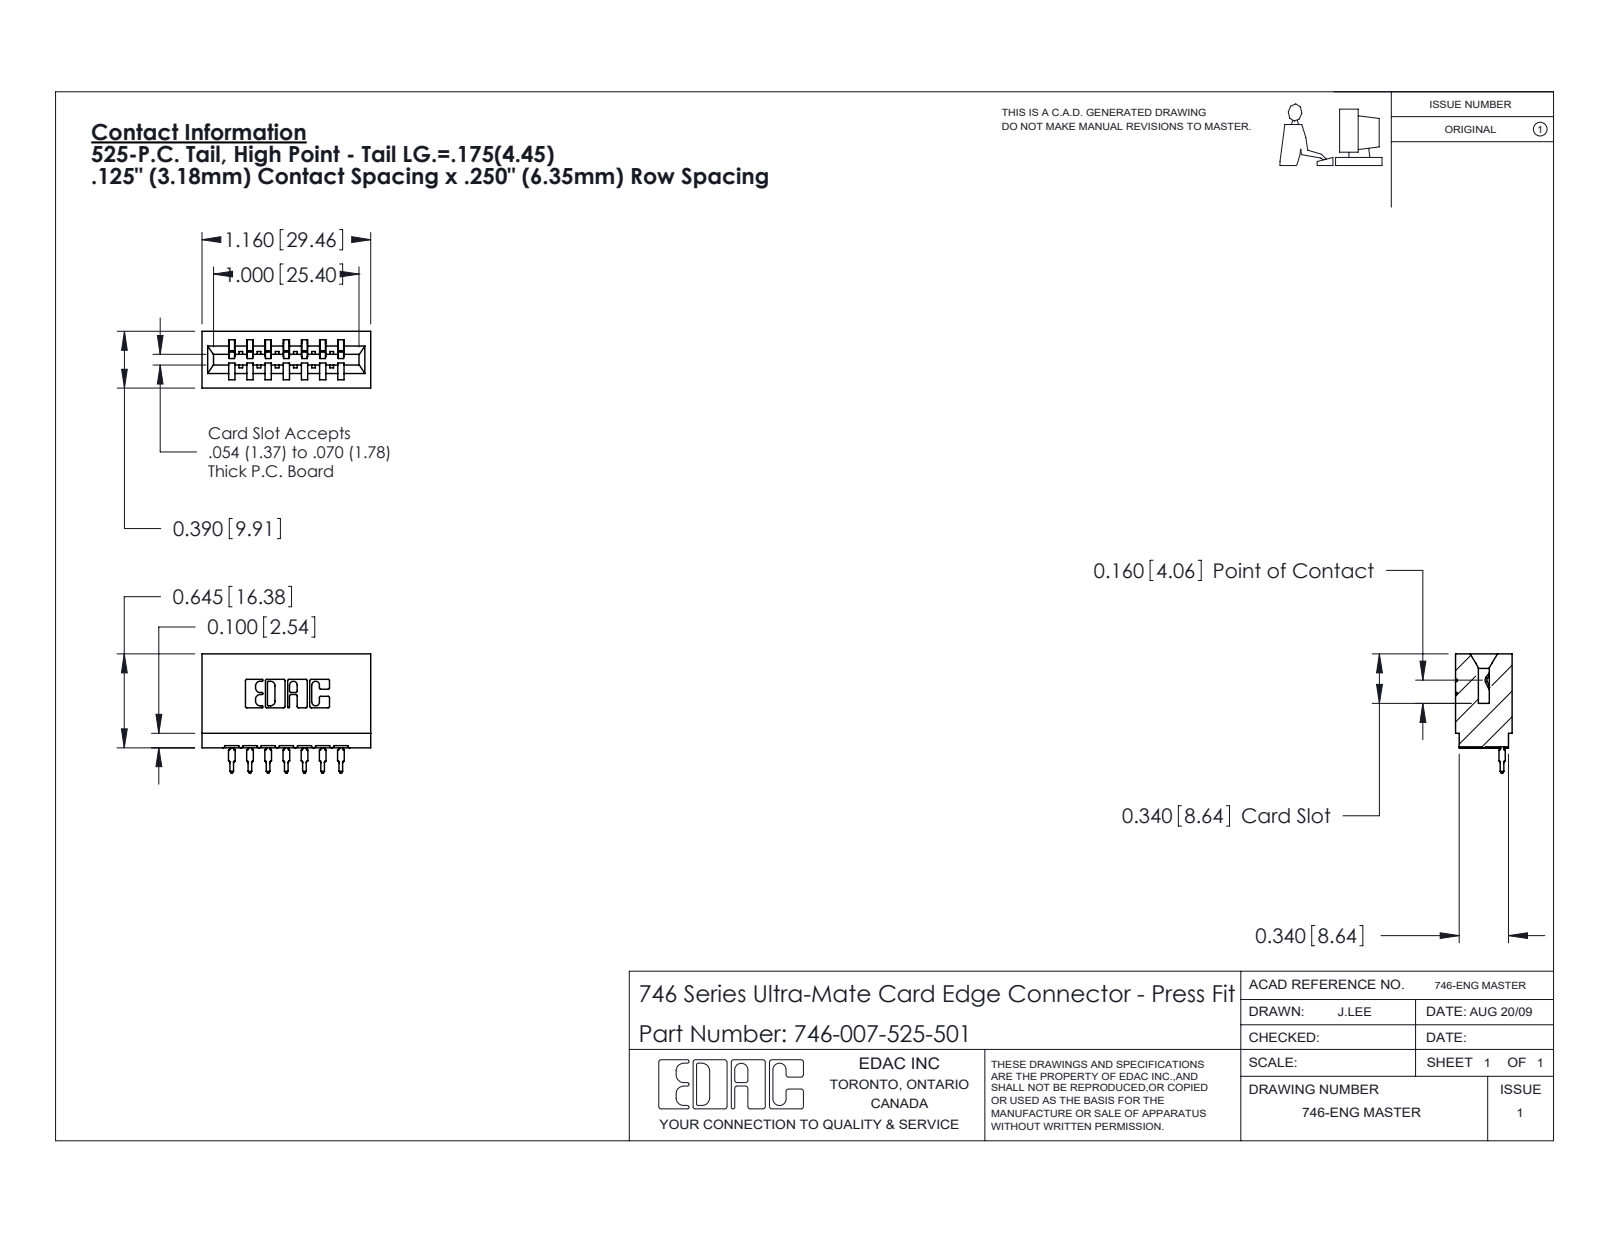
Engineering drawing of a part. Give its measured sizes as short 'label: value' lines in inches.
name: 746-292-001_525; 746-007-525-501; 746 Part_.340 Slot Depth - 01
written by: SolidWorks 2020 (CONFIG_CONTROL_DESIGN)
unit: in
bodies: 8 solids, 853 faces (496 planar, 175 cylindrical, 182 other)
size: 1.16 × 0.819 × 0.39
volume: 0.214 in³; area: 6.46 in²
rounds: 22× R0.01, 14× R0.021, 8× R0.015, 6× R0.007, 6× R0.031, 4× R0.005, 4× R0.011, 3× R0.026
face distances: 0.25, 0.042, 0.333, 0.125, 0.125, 0.5, 0.292, 0.208, 0.057, 0.39
